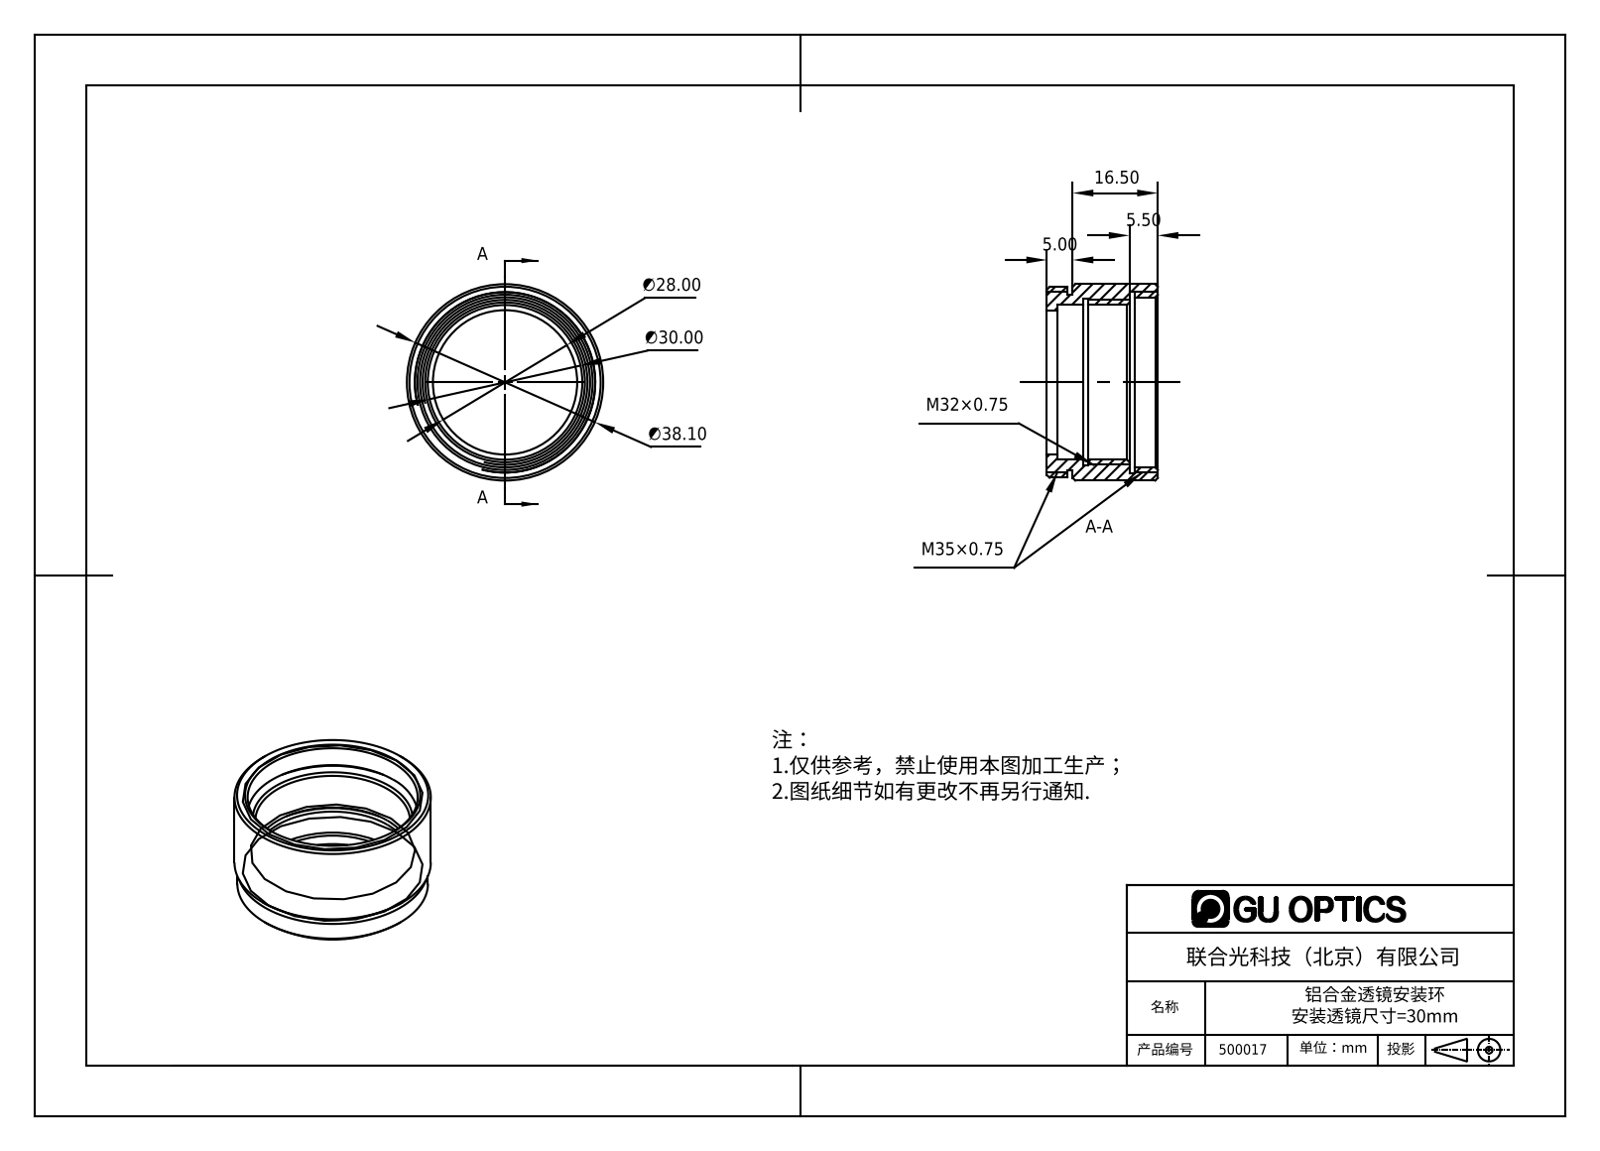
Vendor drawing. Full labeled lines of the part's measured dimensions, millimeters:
Part name (STEP PRODUCT): 500017
STEP written by: SolidWorks 2016 (AUTOMOTIVE_DESIGN)
Units: millimetres
Bodies: 1 solid, 37 faces (9 planar, 18 cylindrical, 10 other)
Overall size (bounding box): 38.1 × 38.1 × 21.5
Volume: 7 884 mm³ · Surface area: 6 319 mm²
Round holes (diameter × count): ⌀28 ×1, ⌀30 ×1, ⌀32.3 ×1, ⌀33 ×1, ⌀35.3 ×1
Round bosses / shafts (diameter × count): ⌀38.1 ×1, ⌀37 ×1, ⌀34 ×1
Main face-to-face distances: 1, 3, 2, 12, 4, 5, 8, 9, 16, 21.5
